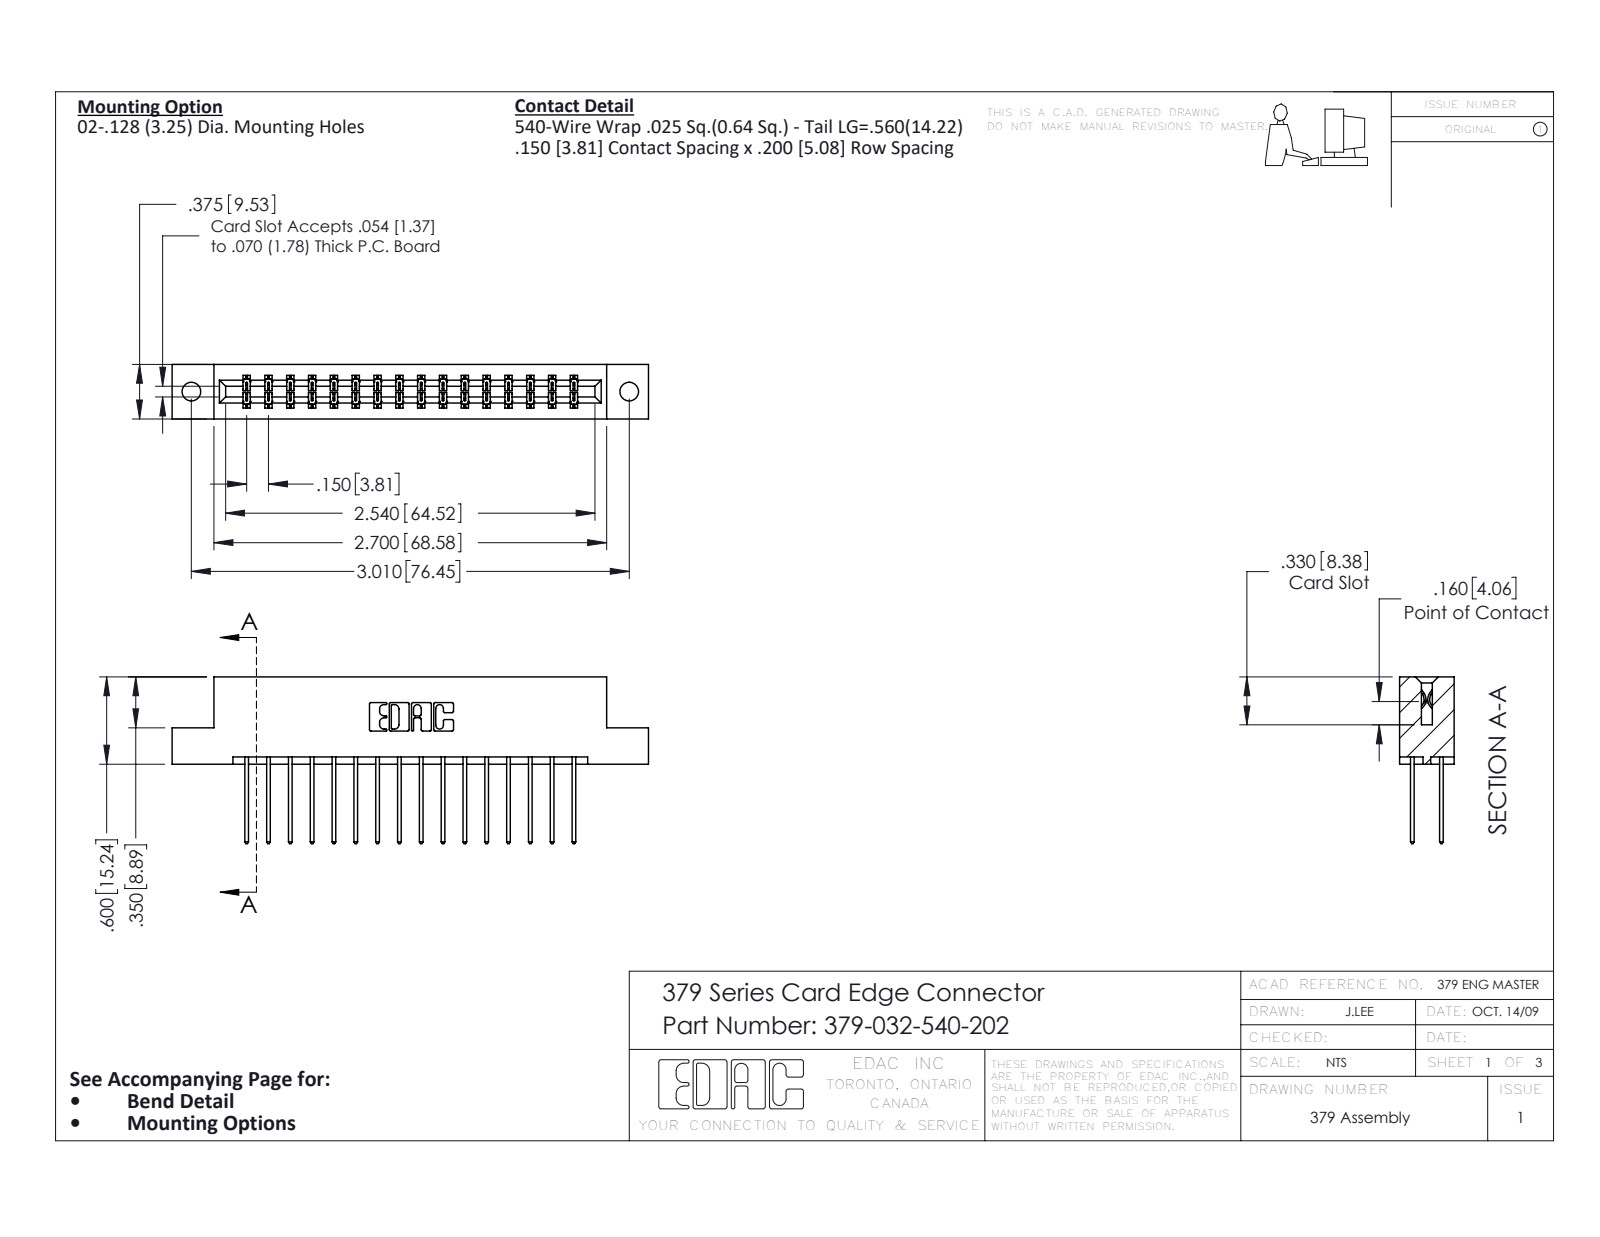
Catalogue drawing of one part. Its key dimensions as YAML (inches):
part_name: "379-032-540-202; 345-292-001_345-293-140; 379 Part_Flush - .128 Dia"
step_written_by: "SolidWorks 2020 (CONFIG_CONTROL_DESIGN)"
units: inches
bodies: {solids: 33, faces: 1778, planar: 1222, cylindrical: 556, other: 0}
overall_size: [3.275, 1.147, 0.375]
volume: 0.526
surface_area: 15.14
round_holes:
  - {diameter: 0.128, count: 2}
partial_cylinders:
  - {radius: 0.006, count: 48}
  - {radius: 0.01, count: 32}
  - {radius: 0.01, count: 22}
  - {radius: 0.007, count: 6}
  - {radius: 0.031, count: 6}
  - {radius: 0.026, count: 3}
  - {radius: 0.014, count: 2}
  - {radius: 0.022, count: 2}
face_to_face_distances: [0.3, 0.075, 0.375, 0.2, 0.1, 0.6, 0.275, 0.15, 0.025, 0.15]
hole_center_spacings: [3.01]
